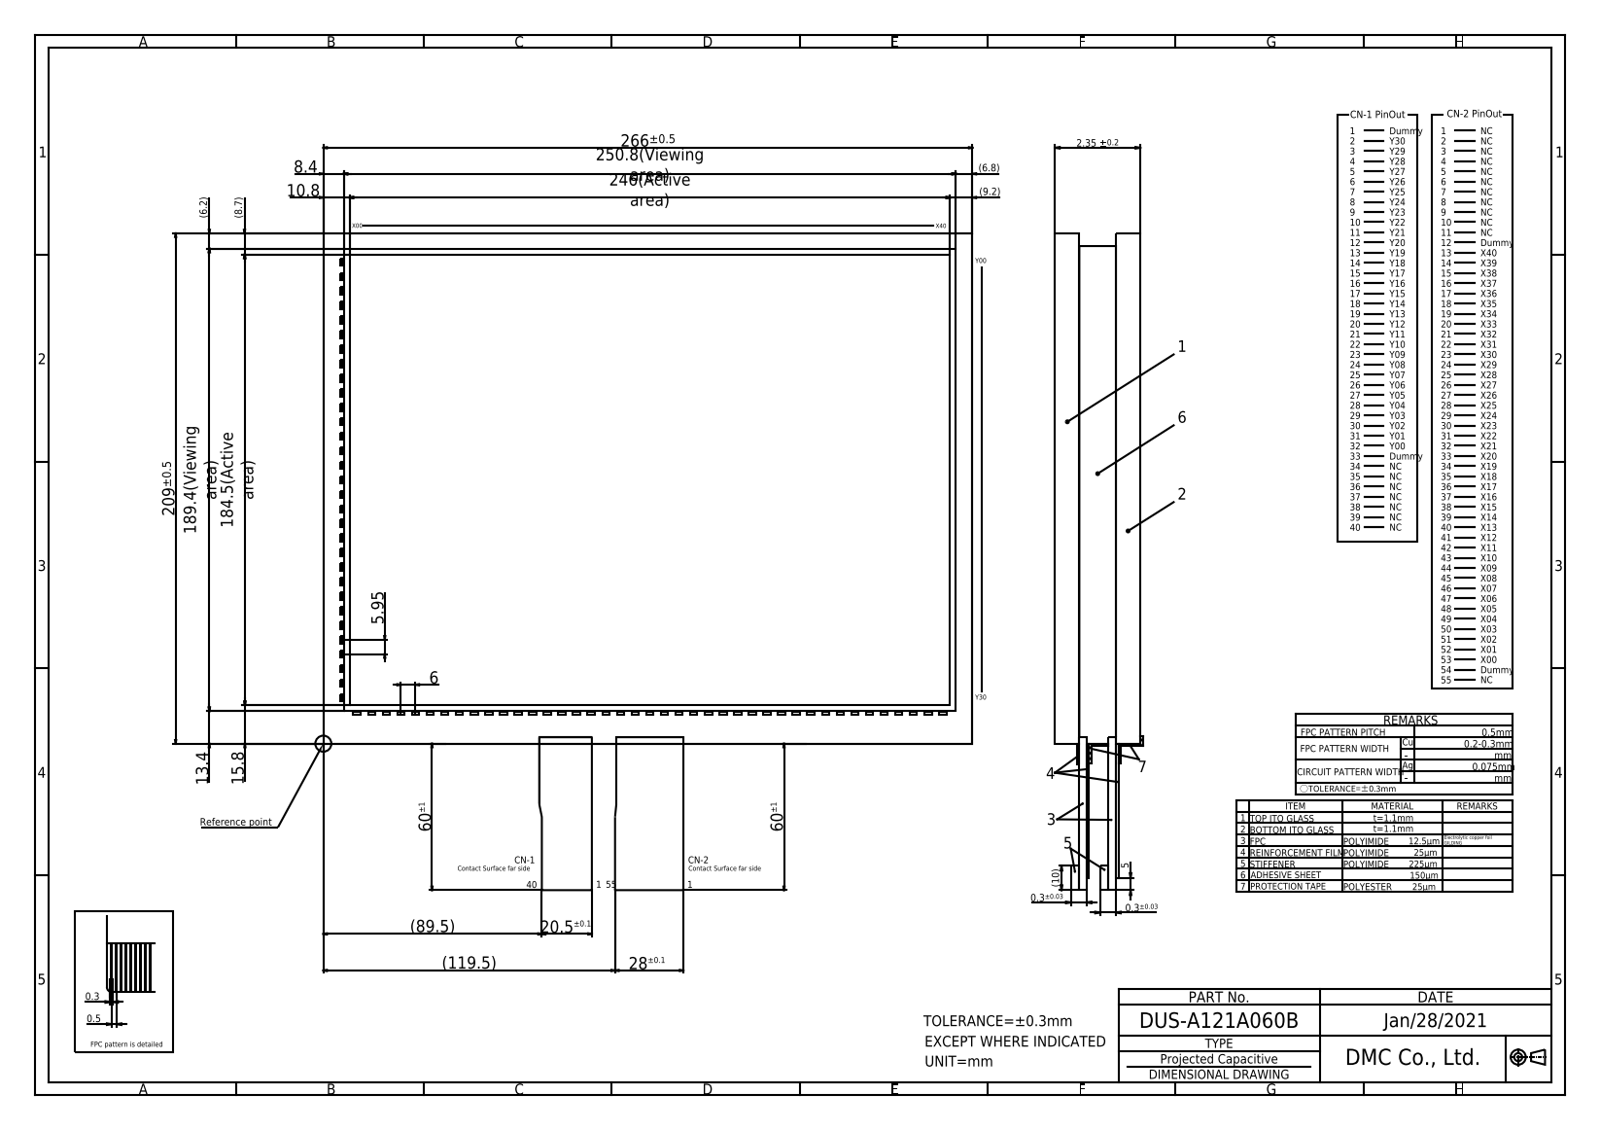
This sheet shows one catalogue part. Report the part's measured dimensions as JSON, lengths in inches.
{"part_name": "DUS-A121A060B", "step_written_by": "Autodesk Inventor 2020 (CONFIG_CONTROL_DESIGN)", "units": "inches", "bodies": {"solids": 1, "faces": 422, "planar": 418, "cylindrical": 4, "other": 0}, "overall_size": [14.661, 12.236, 0.093], "volume_in3": 7.985, "surface_area_in2": 185.2, "partial_cylinders_radius": [[0.008, 4]], "face_to_face_distances": [0.093, 0.043, 0.045, 0.047, 0.049, 0.039, 0.089, 8.228, 10.472, 0.031]}
